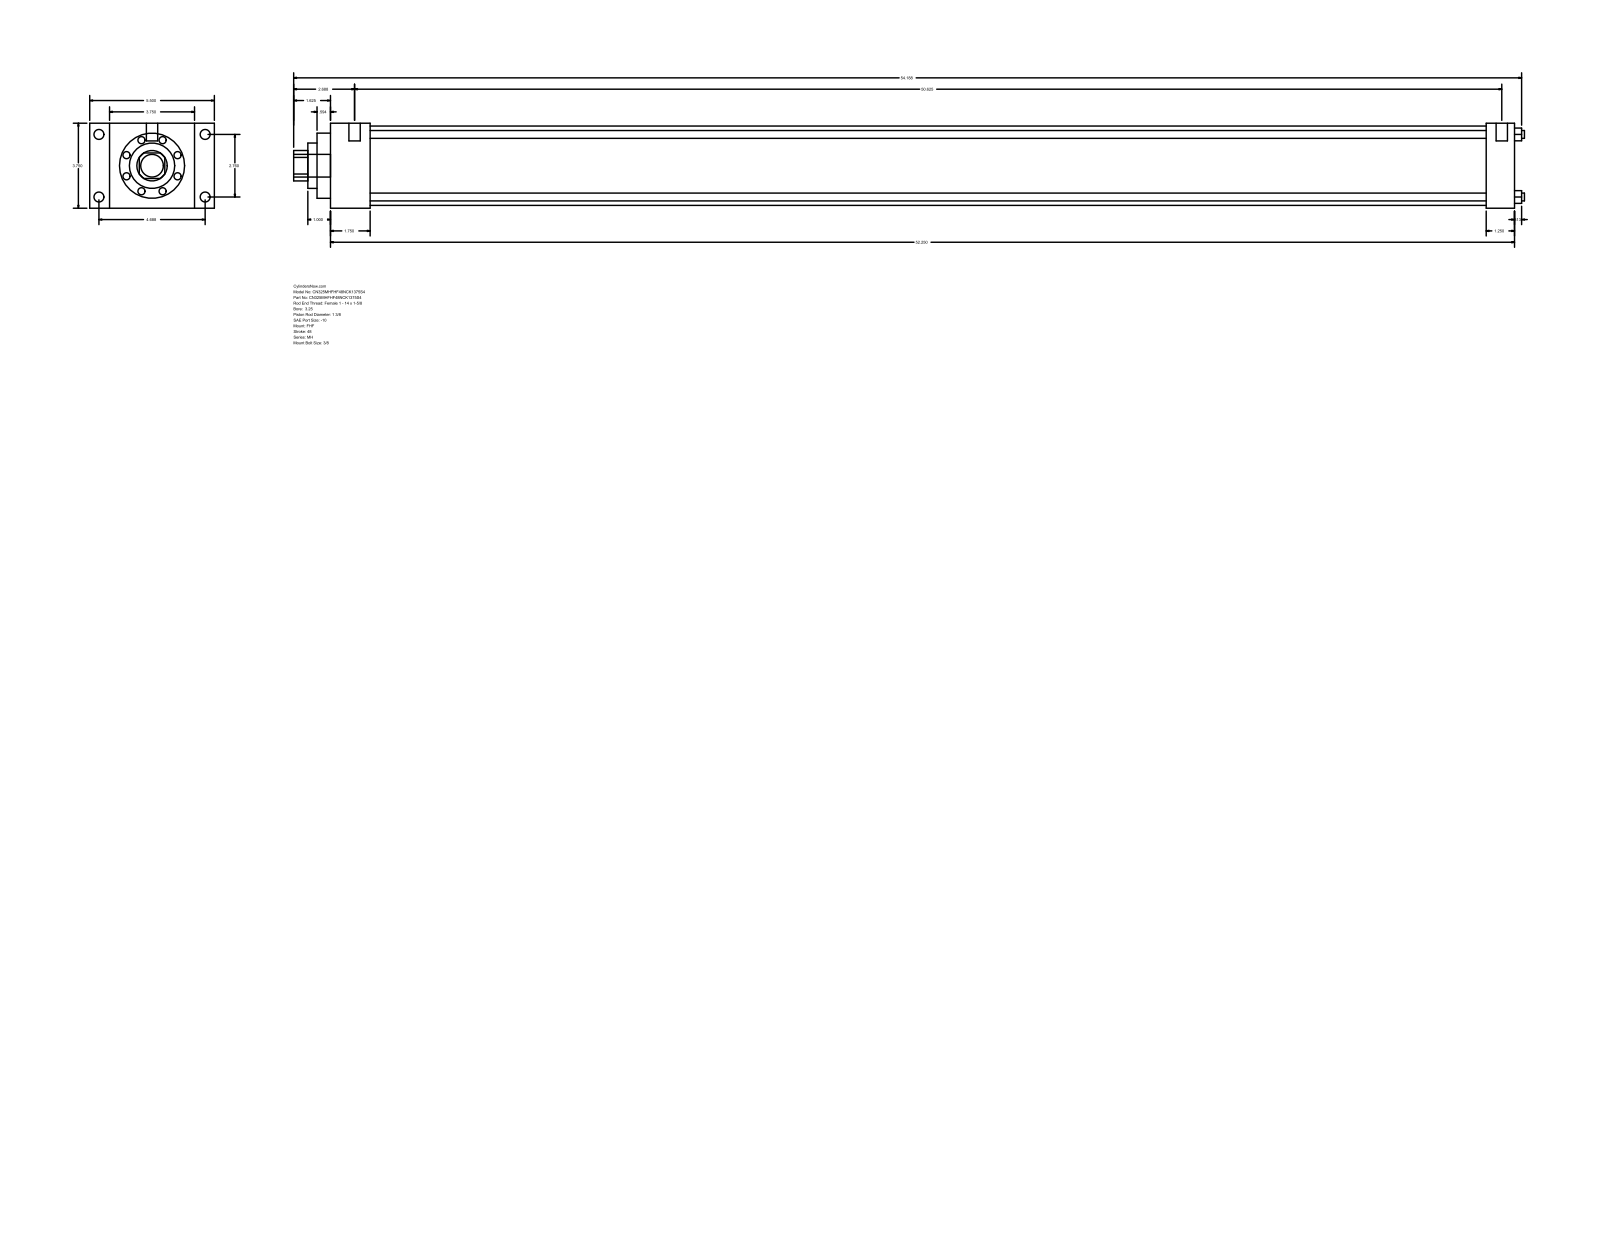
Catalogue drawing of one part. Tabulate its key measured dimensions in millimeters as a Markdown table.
| quantity | value |
| --- | --- |
| part name | MH_FHF__0325_1.375 |
| STEP written by | GSSL Pune (CONFIG_CONTROL_DESIGN) |
| units | millimeters |
| bodies | 0 solids, 90 faces (61 planar, 29 cylindrical, 0 other) |
| overall size | 1379.54 × 139.7 × 95.25 |
| round holes (diameter × count) | 8.76 × 4, 34.92 × 1, 50.8 × 1, 73.03 × 1, 88.9 × 1 |
| round bosses / shafts (diameter × count) | 11.13 × 4, 5.56 × 4, 12.7 × 2, 25.4 × 1 |
| partial cylindrical surfaces (radius × count) | 17.06 × 1 |
| main face-to-face distances | 95.24, 1327.15, 44.45, 1282.7, 22.23, 117.47, 139.7, 1295.4, 1250.95, 31.75 |
| hole center spacings | 49.57, 70.1, 99.14 |
